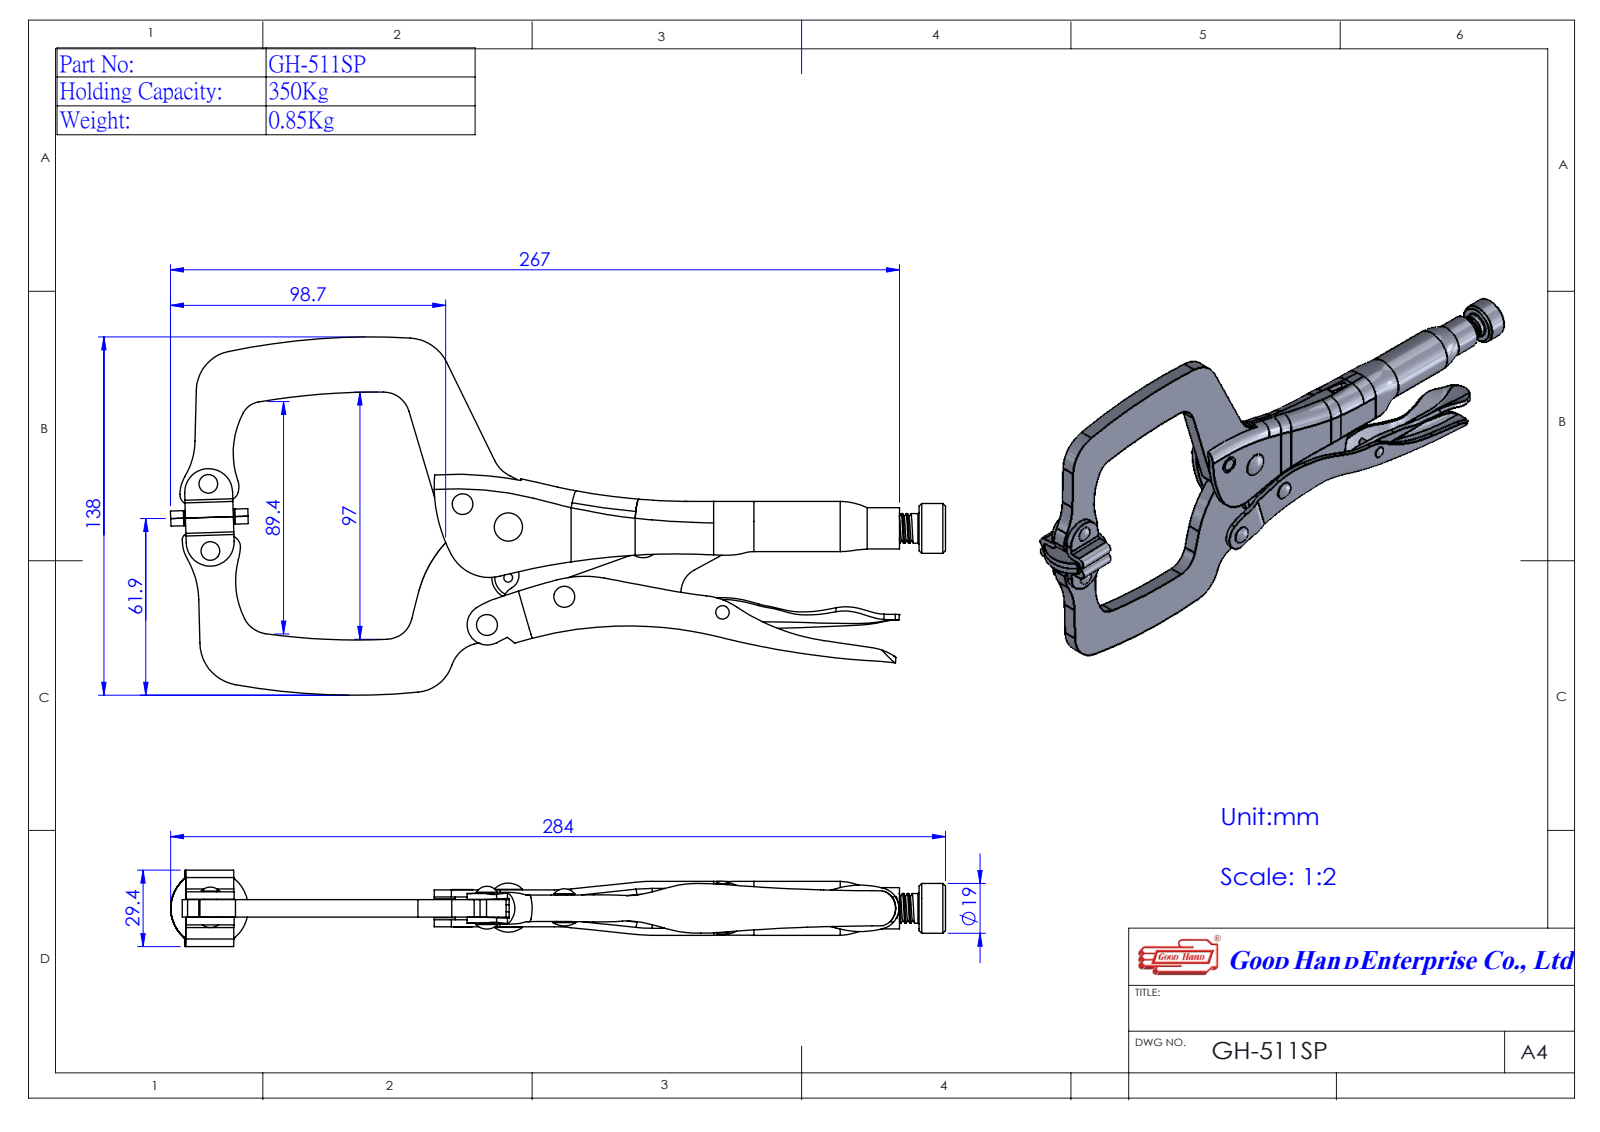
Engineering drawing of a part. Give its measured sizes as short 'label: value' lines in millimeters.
name: GH-511SP(單一零件); Group1^GH-511SP(單一零件)
written by: SolidWorks 2016 (AUTOMOTIVE_DESIGN)
unit: mm
bodies: 3 solids, 528 faces (104 planar, 288 cylindrical, 136 other)
size: 287.42 × 132.92 × 28.39
volume: 107 389 mm³; area: 67 923 mm²
holes: 1× ⌀11.81, 1× ⌀14.8
bosses: 3× ⌀1.2, 2× ⌀7.8, 2× ⌀5.4, 2× ⌀4.8, 1× ⌀20, 1× ⌀18.5, 1× ⌀15.3, 1× ⌀11
rounds: 8× R2, 6× R1, 6× R3.8, 4× R2.81, 4× R60, 3× R16, 2× R2.4, 2× R4.4
face distances: 6.5, 2.6, 5.55, 1, 1.95, 0.95, 6.55, 7.5, 3.6, 4.55
